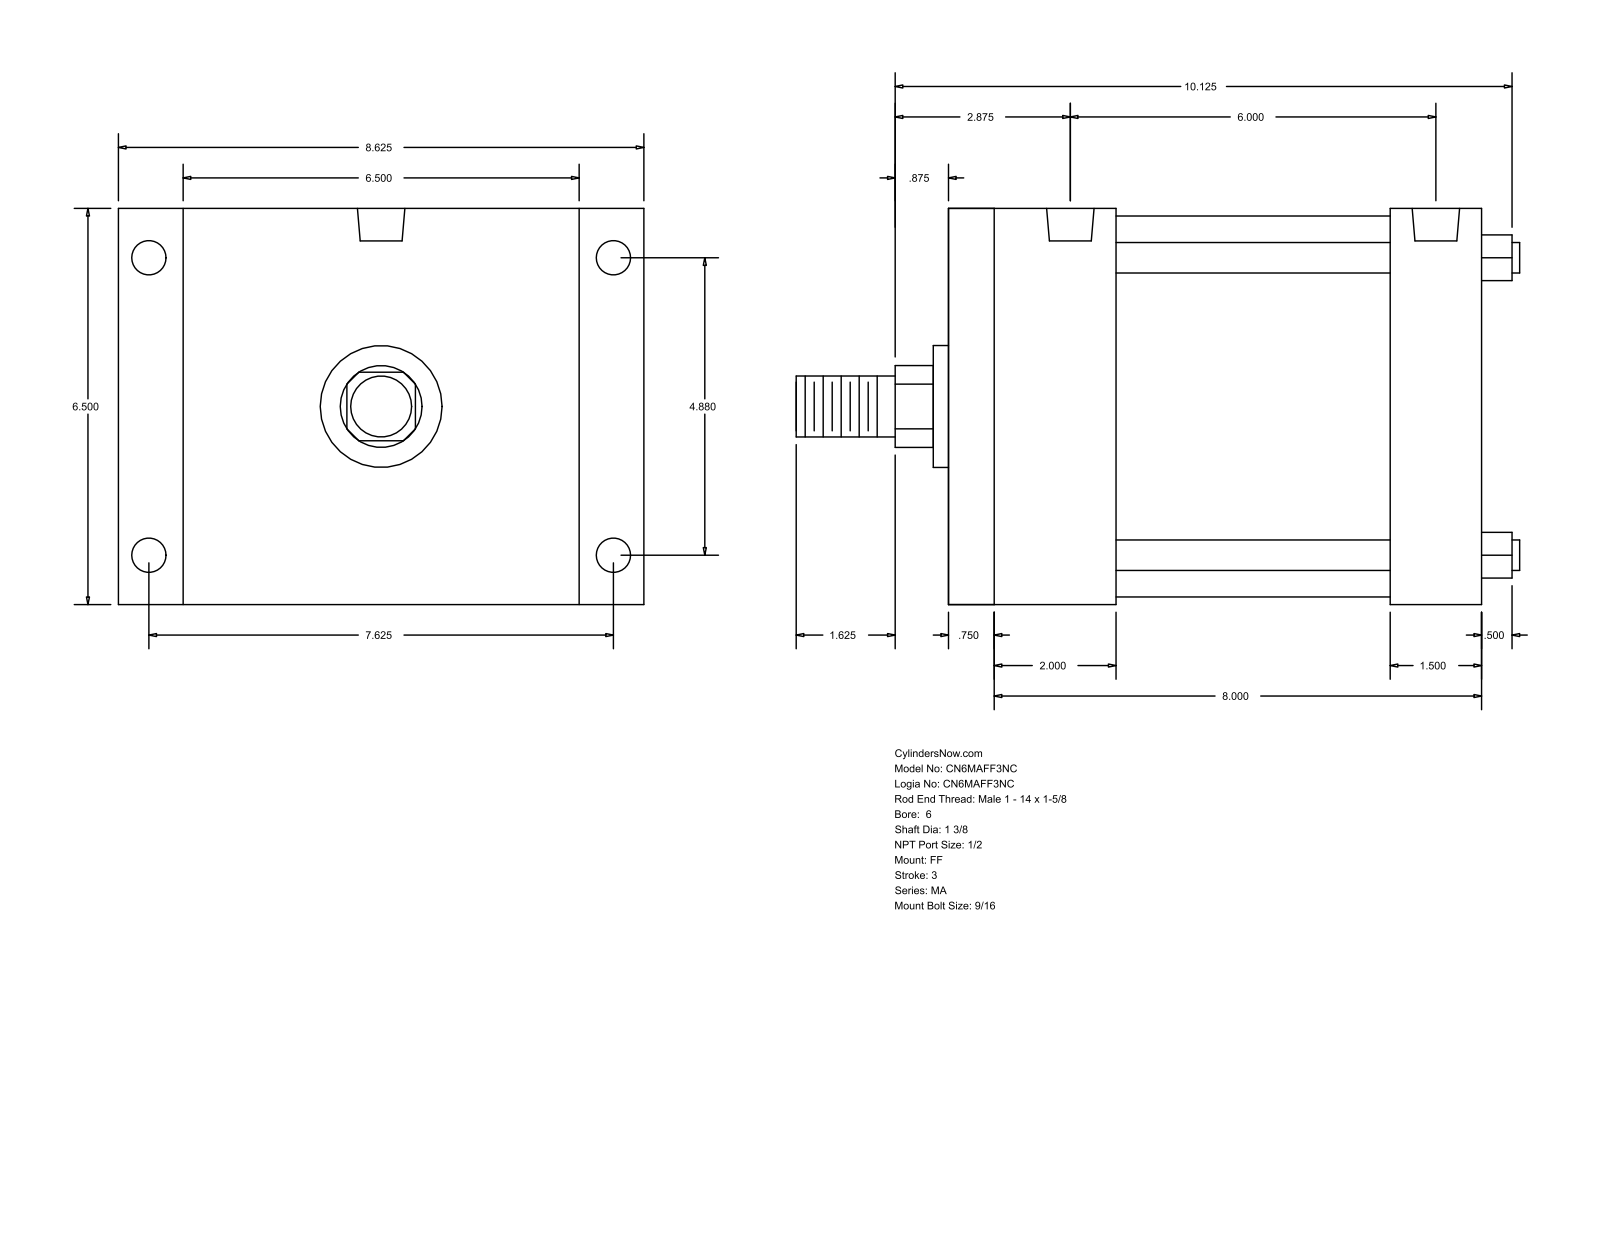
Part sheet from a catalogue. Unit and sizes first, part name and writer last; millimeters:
Units: millimetres
Overall size (bounding box): 301.62 × 219.07 × 165.1
Round holes (diameter × count): ⌀14.29 ×4, ⌀17.46 ×4, ⌀19.77 ×2
Round bosses / shafts (diameter × count): ⌀12.7 ×4, ⌀158.75 ×1, ⌀50.8 ×1, ⌀34.92 ×1, ⌀25.4 ×1
Partial cylindrical surfaces — rounded edges, fillets, slot ends (radius × count): R17.06 ×1
Main face-to-face distances: 165.1, 222.24, 15.87, 206.37, 50.8, 168.28, 66.67, 155.57, 184.15, 117.48
Hole centre spacings: 123.96, 155.58, 193.68, 229.95, 3.18, 152.4
Bodies: 0 solids, 92 faces (64 planar, 28 cylindrical, 0 other)
Part name (STEP PRODUCT): MA_FF__0600_1.375
STEP written by: GSSL Pune (CONFIG_CONTROL_DESIGN)
